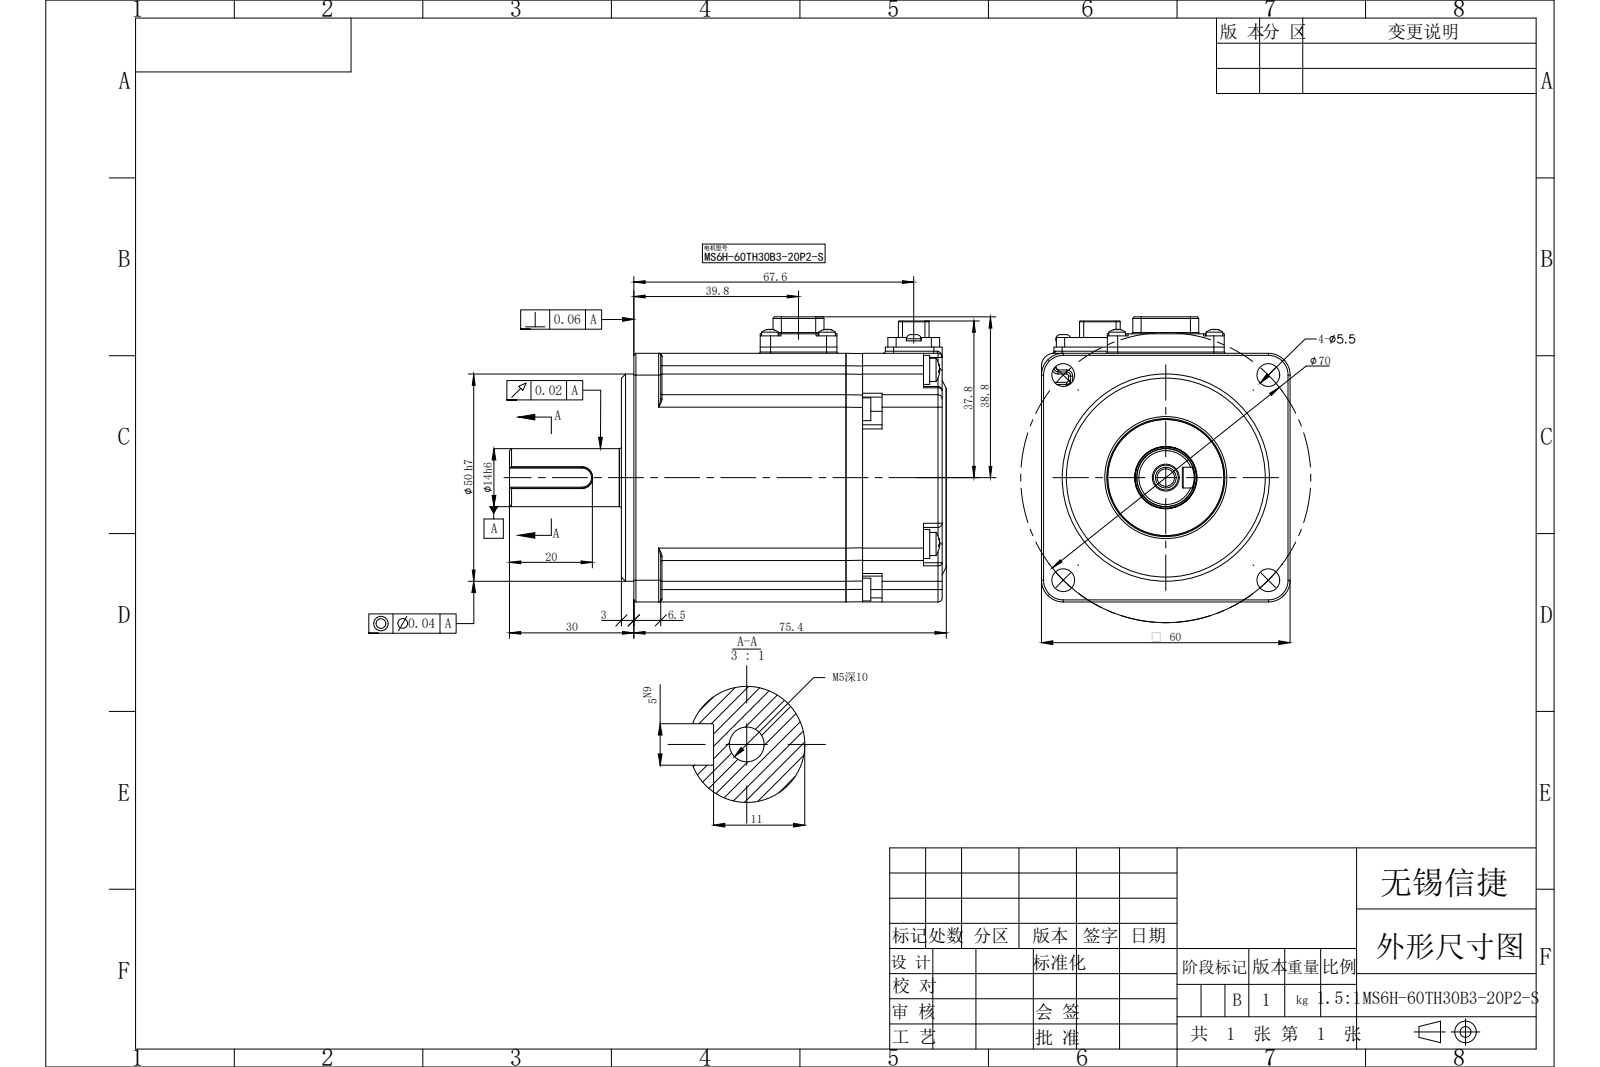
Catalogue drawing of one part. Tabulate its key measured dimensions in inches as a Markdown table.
| quantity | value |
| --- | --- |
| part name | MS6H-60TH30B3-20P2-S |
| STEP written by | SolidWorks 2022 (CONFIG_CONTROL_DESIGN) |
| units | inches |
| bodies | 0 solids, 806 faces (391 planar, 277 cylindrical, 138 other) |
| overall size | 4.15 × 2.709 × 2.362 |
| round holes (diameter × count) | 0.083 × 4, 0.217 × 4, 0.063 × 2, 0.165 × 1, 0.197 × 1, 0.591 × 1 |
| round bosses / shafts (diameter × count) | 0.276 × 4, 0.22 × 4, 0.217 × 4, 0.157 × 4, 0.138 × 2, 1.969 × 1, 1.102 × 1, 0.583 × 1 |
| partial cylindrical surfaces (radius × count) | 0.039 × 39, 0.02 × 24, 0.008 × 21, 0.012 × 21, 0.118 × 17, 0.079 × 12, 0.018 × 11, 0.197 × 8 |
| main face-to-face distances | 2.362, 2.969, 2.929, 0.118, 0.039, 3.087, 3.047, 0.394, 0.795, 0.756 |
| hole center spacings | 1.378, 1.949, 0.315, 0.654, 0.726, 2.756, 0.925, 0.951 |
